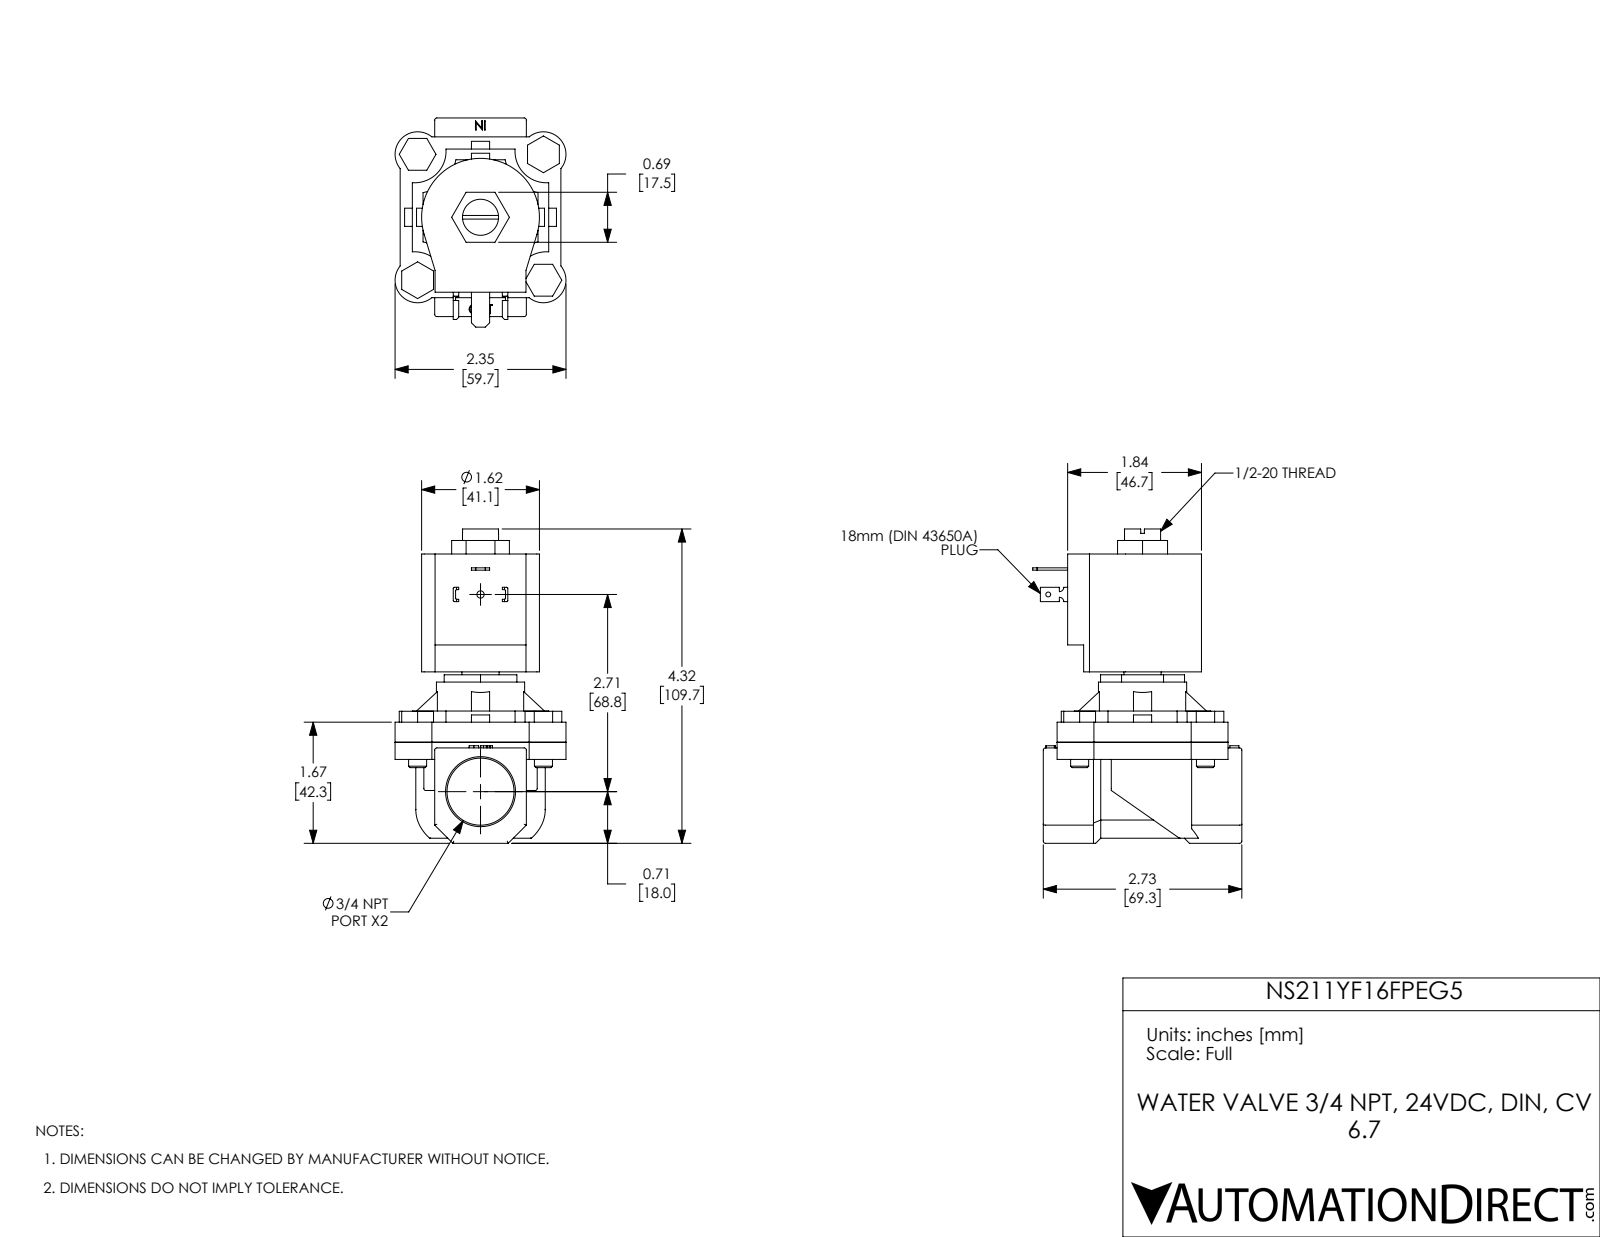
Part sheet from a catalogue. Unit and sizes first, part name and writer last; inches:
Units: inches
Overall size (bounding box): 4.32 × 2.875 × 2.35
Round holes (diameter × count): ⌀0.25 ×4, ⌀0.067 ×1, ⌀0.1 ×1, ⌀0.496 ×1, ⌀0.512 ×1, ⌀0.922 ×1, ⌀1.155 ×1
Round bosses / shafts (diameter × count): ⌀0.248 ×4, ⌀1.213 ×1
Partial cylindrical surfaces — rounded edges, fillets, slot ends (radius × count): R0.03 ×15, R0.015 ×8, R0.31 ×4, R0.432 ×4, R0.579 ×4, R0.06 ×2, R0.81 ×1, R0.89 ×1
Main face-to-face distances: 0.276, 2.587, 2.311, 0.236, 0.512, 2.823, 0.475, 1.735, 1.26, 2.21
Hole centre spacings: 1.223, 1.73, 2.446, 2.71
Volume: 10.62 in³ · Surface area: 70.92 in²
Bodies: 11 solids, 387 faces (241 planar, 113 cylindrical, 33 other)
Part name (STEP PRODUCT): NS211YF16FPEG5
STEP written by: SolidWorks 2017 (AUTOMOTIVE_DESIGN)
